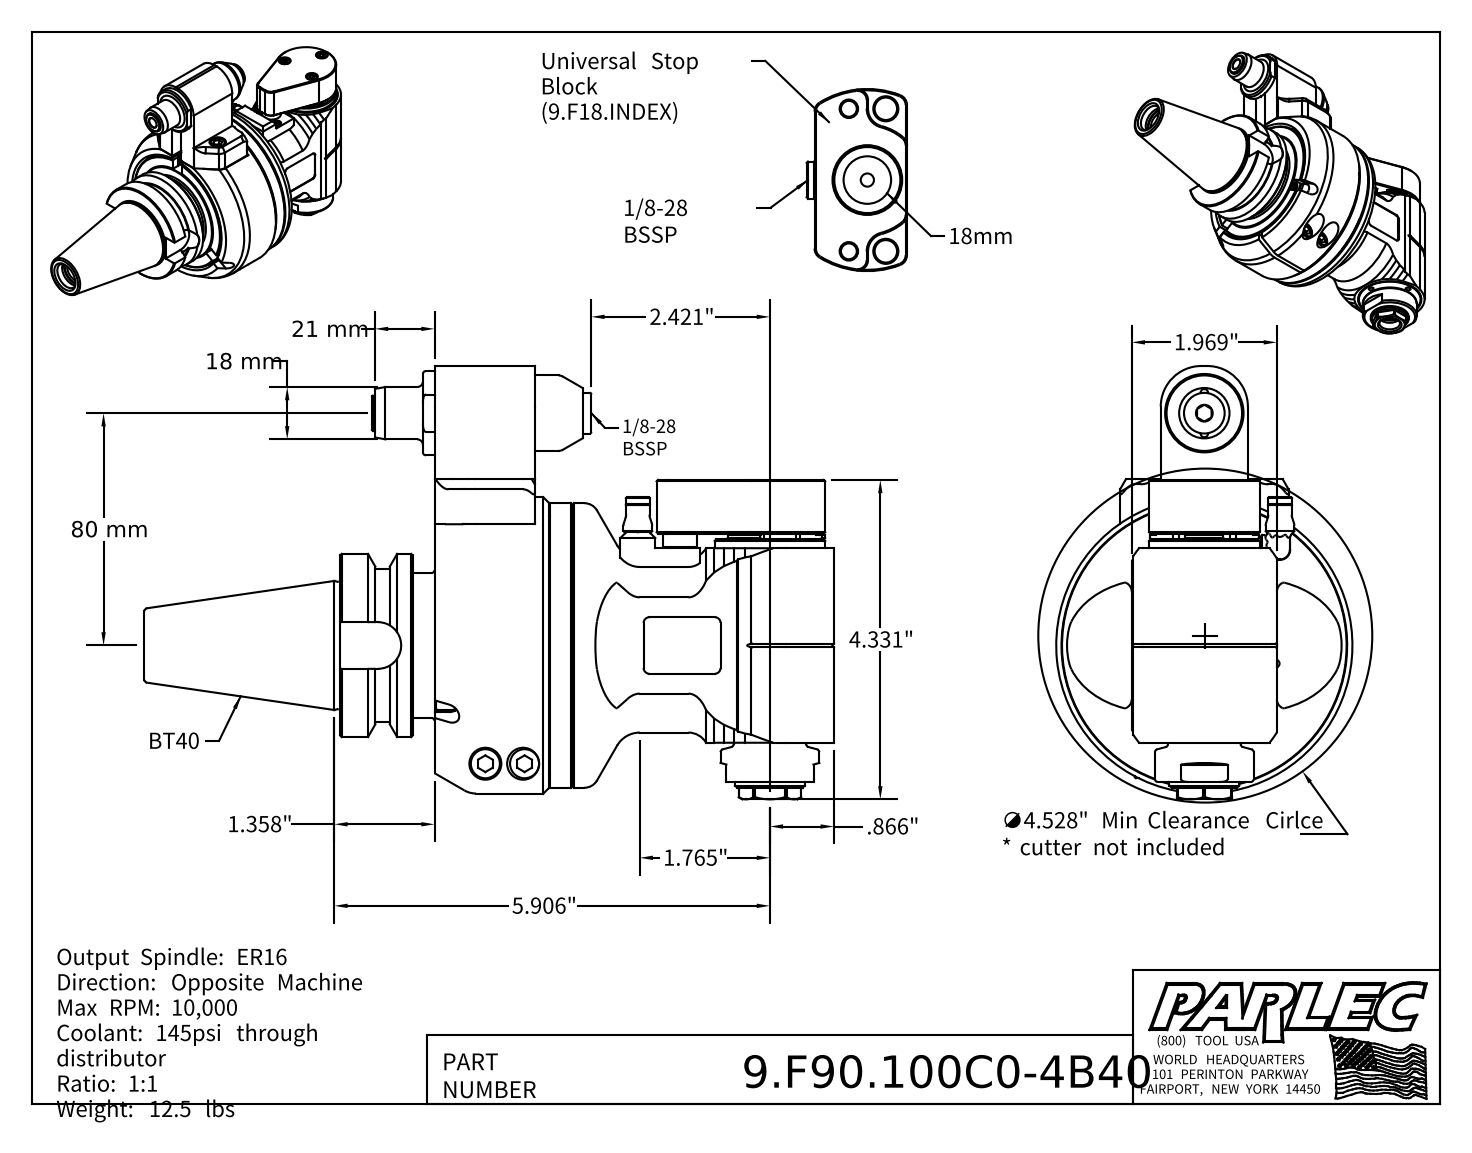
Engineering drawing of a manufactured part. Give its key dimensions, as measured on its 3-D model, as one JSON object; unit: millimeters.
{"part_name": "9.F90.100C0-4B40; 9_F90_100B0; 9_GA1_348_2 (Type 1, BT40, 80mm)", "step_written_by": "Autodesk Inventor 2022 (AUTOMOTIVE_DESIGN)", "units": "millimeters", "bodies": {"solids": 5, "faces": 786, "planar": 344, "cylindrical": 203, "other": 239}, "overall_size": [237.4, 149.3, 102], "volume_mm3": 888000, "surface_area_mm2": 153400, "round_holes": [[8.5, 20], [3.2, 4], [7.5, 3], [11, 3], [2.6, 2], [3.5, 2], [4.2, 2], [5, 2], [6, 2], [10.4, 2], [13, 2], [2.5, 1]], "round_bosses_or_shafts": [[10, 5], [6, 5], [7, 3], [18, 2], [12, 2], [8, 2], [5.5, 2], [2.5, 2]], "partial_cylinders_radius": [[2, 13], [1, 6], [0.5, 4], [3.5, 4], [4, 4], [5, 4], [0.2, 3], [0.4, 2]], "face_to_face_distances": [32, 39.5, 7.5, 0.5, 40, 8, 5, 7, 8.5, 10], "hole_center_spacings": [38.5, 46.3, 76.3, 54.5, 10.7, 37.3, 61.5, 74]}
